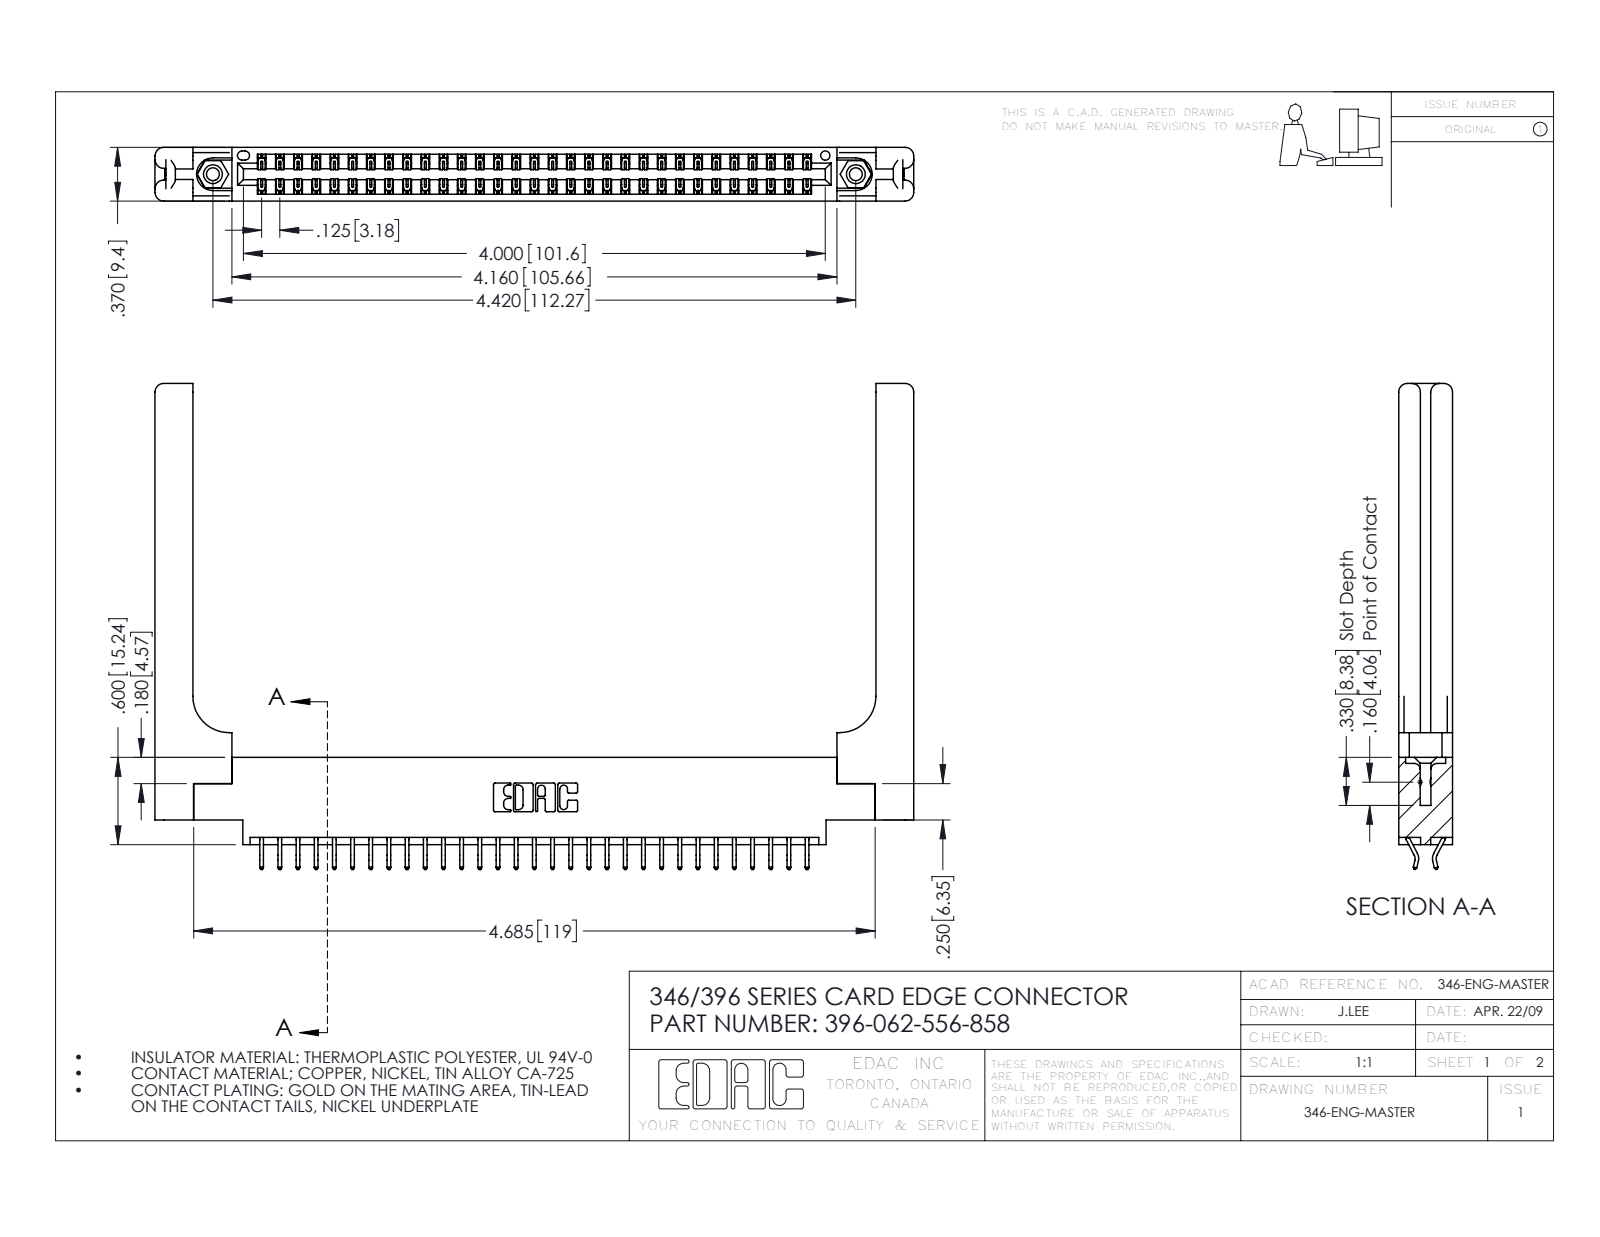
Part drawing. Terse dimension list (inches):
name: 396-062-556-858; 345-250-001_345-250-001-102; 346 Part_0.170 Offset - 0.156 Dia-TH; 345-292-001_556 Tail (+1 more)
written by: SolidWorks 2016 (CONFIG_CONTROL_DESIGN)
unit: in
bodies: 67 solids, 3978 faces (2646 planar, 1272 cylindrical, 60 other)
size: 5.216 × 3.34 × 0.37
volume: 1.231 in³; area: 34.64 in²
holes: 2× ⌀0.089, 2× ⌀0.125, 2× ⌀0.156, 1× ⌀0.064
bosses: 2× ⌀0.155
rounds: 93× R0.006, 22× R0.01, 16× R0.06, 6× R0.007, 6× R0.031, 3× R0.026, 2× R0.01, 2× R0.014
face distances: 0.37, 0.048, 0.322, 0.072, 0.148, 0.15, 0.25, 0.025, 0.298, 0.275
hole spacings: 0.246, 4.212, 4.42
